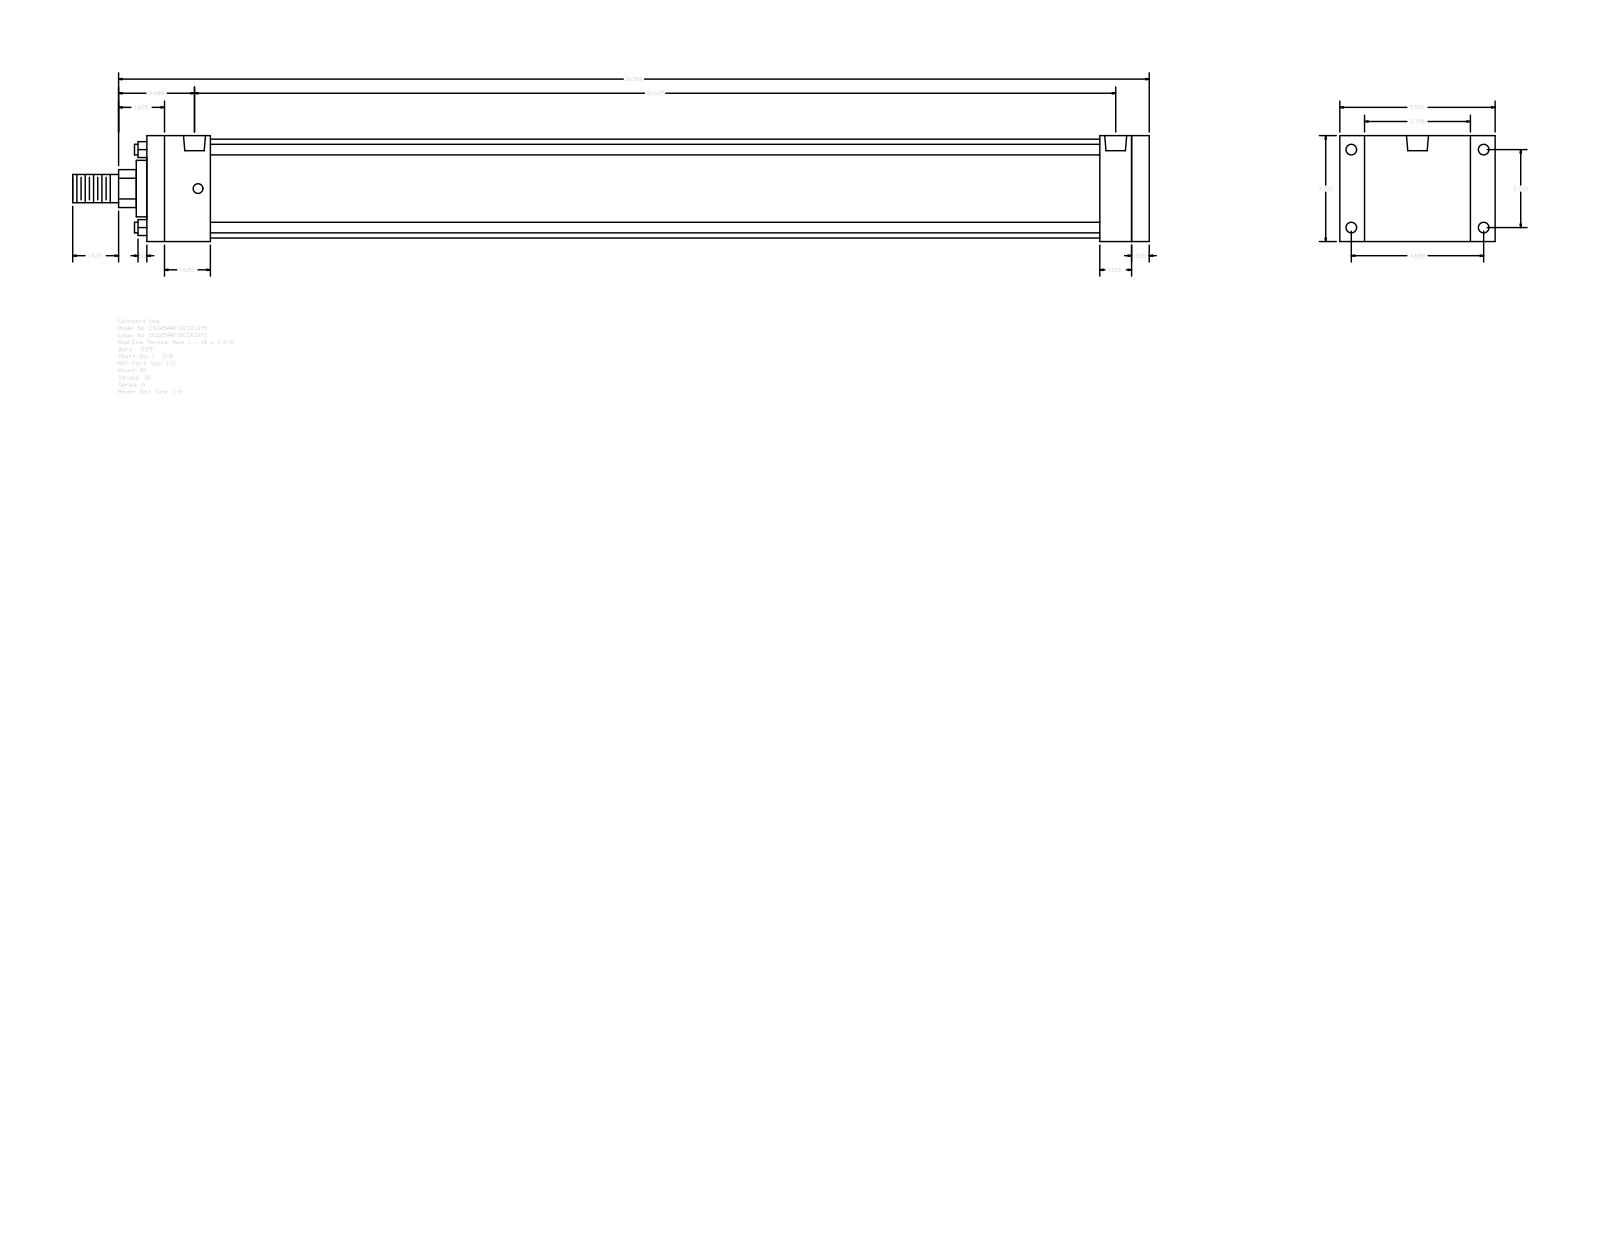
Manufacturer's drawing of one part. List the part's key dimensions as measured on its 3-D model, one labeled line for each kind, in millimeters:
Part name (STEP PRODUCT): A_RF__0325_1.375
STEP written by: GSSL Pune (CONFIG_CONTROL_DESIGN)
Units: millimetres
Bodies: 0 solids, 92 faces (64 planar, 28 cylindrical, 0 other)
Overall size (bounding box): 968.38 × 139.7 × 95.25
Round holes (diameter × count): ⌀8.73 ×4, ⌀9.53 ×4, ⌀19.77 ×2
Round bosses / shafts (diameter × count): ⌀9.53 ×4, ⌀88.9 ×1, ⌀50.8 ×1, ⌀34.92 ×1, ⌀25.4 ×1
Partial cylindrical surfaces — rounded edges, fillets, slot ends (radius × count): R17.06 ×1
Main face-to-face distances: 95.24, 901.7, 885.83, 15.87, 57.15, 28.58, 22.23, 117.47, 857.25, 44.45
Hole centre spacings: 3.18, 70.1, 119.06, 138.16, 822.32, 825.5, 828.68
